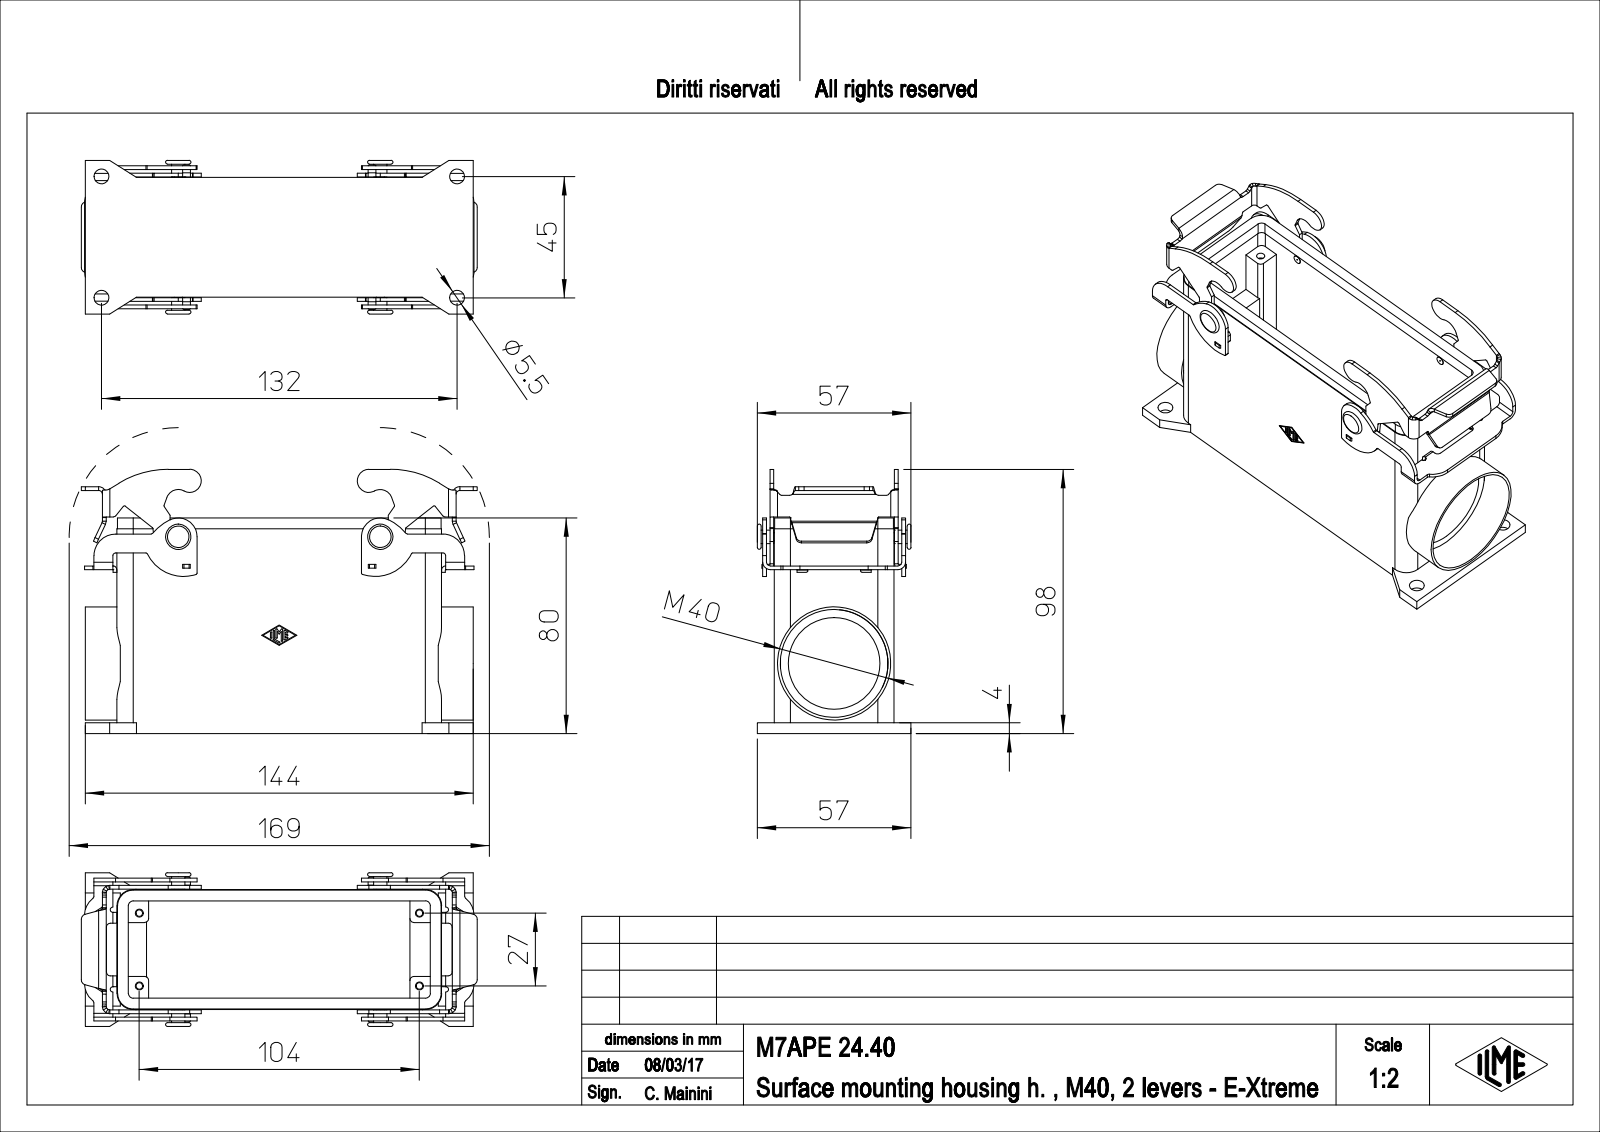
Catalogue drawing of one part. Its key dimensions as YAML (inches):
part_name: "M7APE_24.40"
step_written_by: "PTC Creo Elements/Direct Modeling 19.0E 27-Jun-2016 (C) Parametric Technology GmbH (AUTOMOTIVE_DESIGN)"
units: inches
bodies: {solids: 1, faces: 615, planar: 299, cylindrical: 270, other: 46}
overall_size: [5.786, 3.858, 2.244]
volume: 8.783
surface_area: 131.3
round_holes:
  - {diameter: 0.097, count: 4}
  - {diameter: 0.118, count: 4}
  - {diameter: 0.217, count: 4}
  - {diameter: 0.138, count: 2}
  - {diameter: 1.339, count: 1}
  - {diameter: 1.575, count: 1}
round_bosses_or_shafts:
  - {diameter: 0.197, count: 2}
  - {diameter: 0.126, count: 2}
  - {diameter: 0.118, count: 2}
  - {diameter: 1.654, count: 1}
partial_cylinders:
  - {radius: 0.02, count: 22}
  - {radius: 0.039, count: 18}
  - {radius: 0.01, count: 16}
  - {radius: 0.059, count: 14}
  - {radius: 0.079, count: 12}
  - {radius: 0.055, count: 10}
  - {radius: 0.11, count: 10}
  - {radius: 0.315, count: 6}
face_to_face_distances: [0.157, 1.594, 1.752, 1.437, 0.055, 0.106, 1.925, 0.325, 0.463, 0.167]
hole_center_spacings: [0.655, 1.521, 4.659, 4.857, 1.063, 1.772, 4.094, 4.23]
